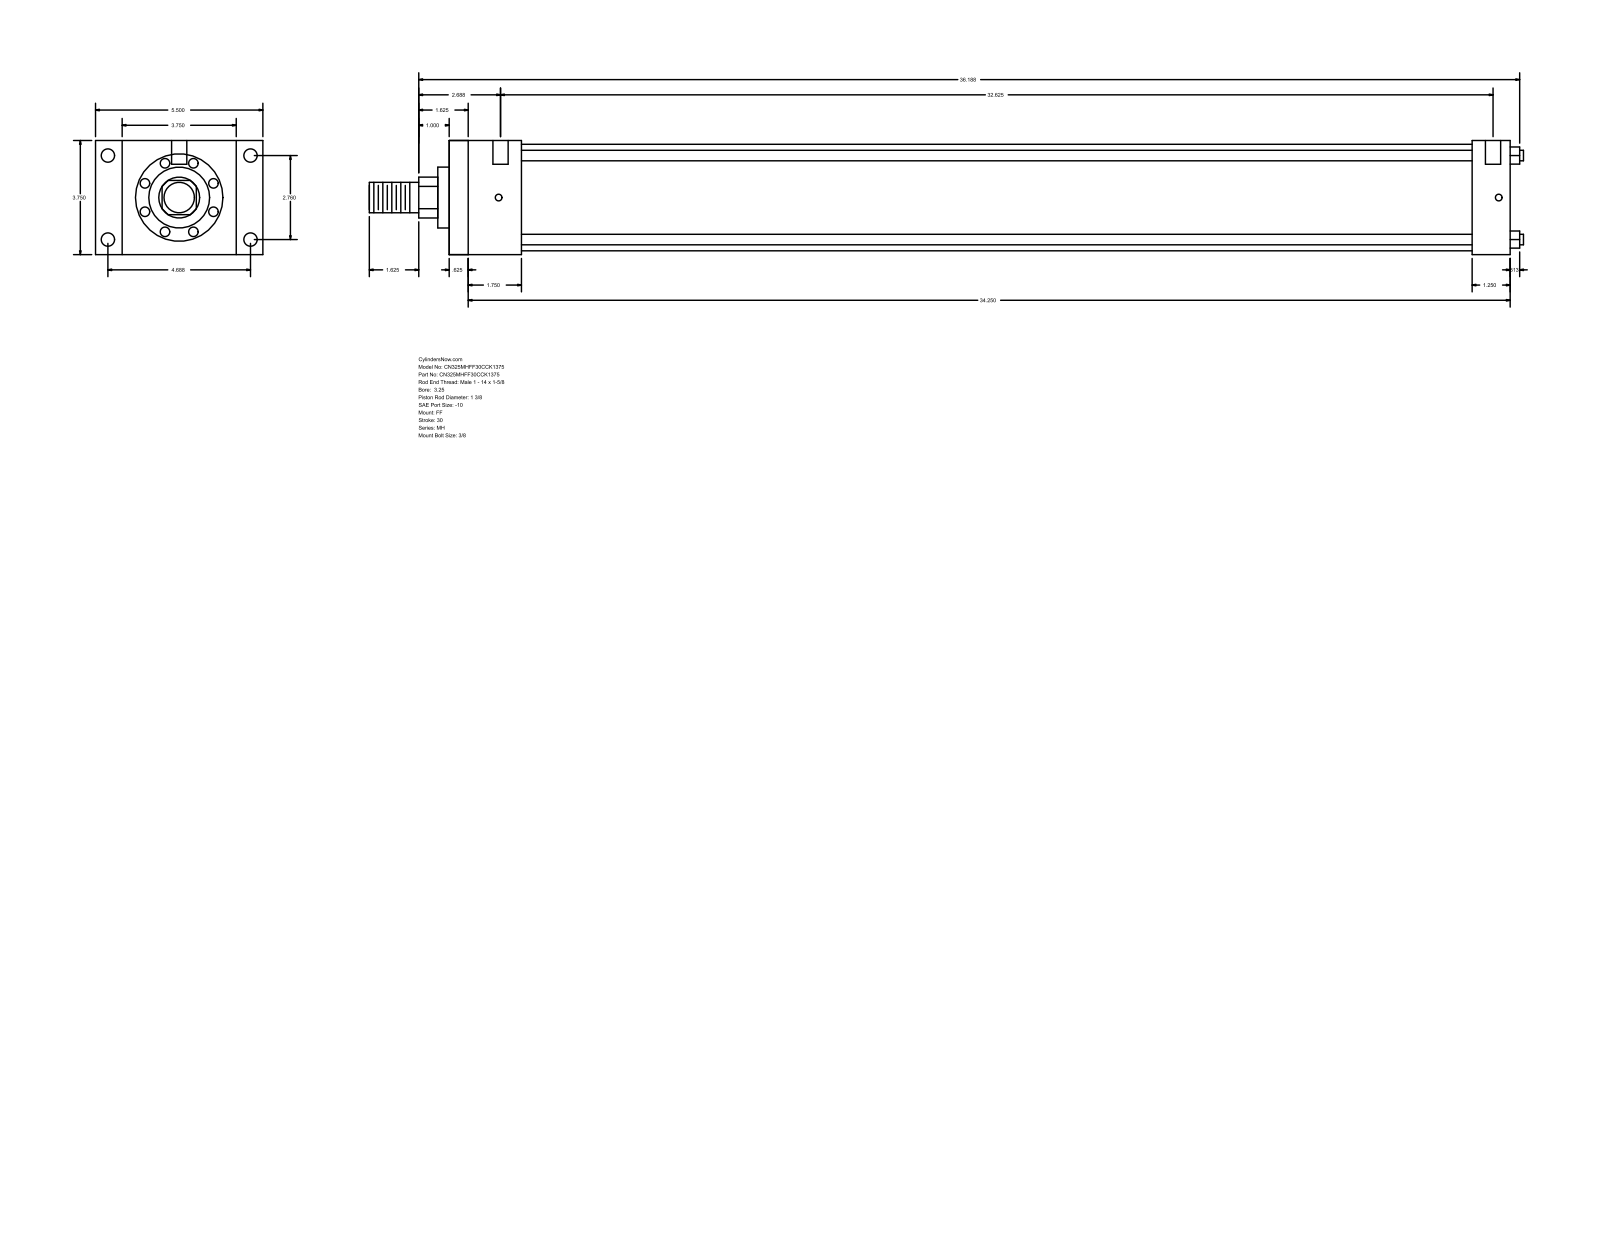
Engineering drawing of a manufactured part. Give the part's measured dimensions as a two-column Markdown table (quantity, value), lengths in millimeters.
| quantity | value |
| --- | --- |
| part name | MH_FF__0325_1.375 |
| STEP written by | GSSL Pune (CONFIG_CONTROL_DESIGN) |
| units | millimeters |
| bodies | 0 solids, 92 faces (64 planar, 28 cylindrical, 0 other) |
| overall size | 963.61 × 139.7 × 95.25 |
| round holes (diameter × count) | 5.56 × 4, 11.13 × 4, 12.7 × 2 |
| round bosses / shafts (diameter × count) | 8.76 × 4, 88.9 × 1, 50.8 × 1, 34.92 × 1, 25.4 × 1 |
| partial cylindrical surfaces (radius × count) | 17.06 × 1 |
| main face-to-face distances | 95.24, 885.83, 15.87, 869.96, 22.23, 117.47, 854.08, 838.21, 31.75, 60.32 |
| hole center spacings | 70.1, 119.06, 138.16, 835.03, 1.59, 4.76, 828.68, 830.27 |
